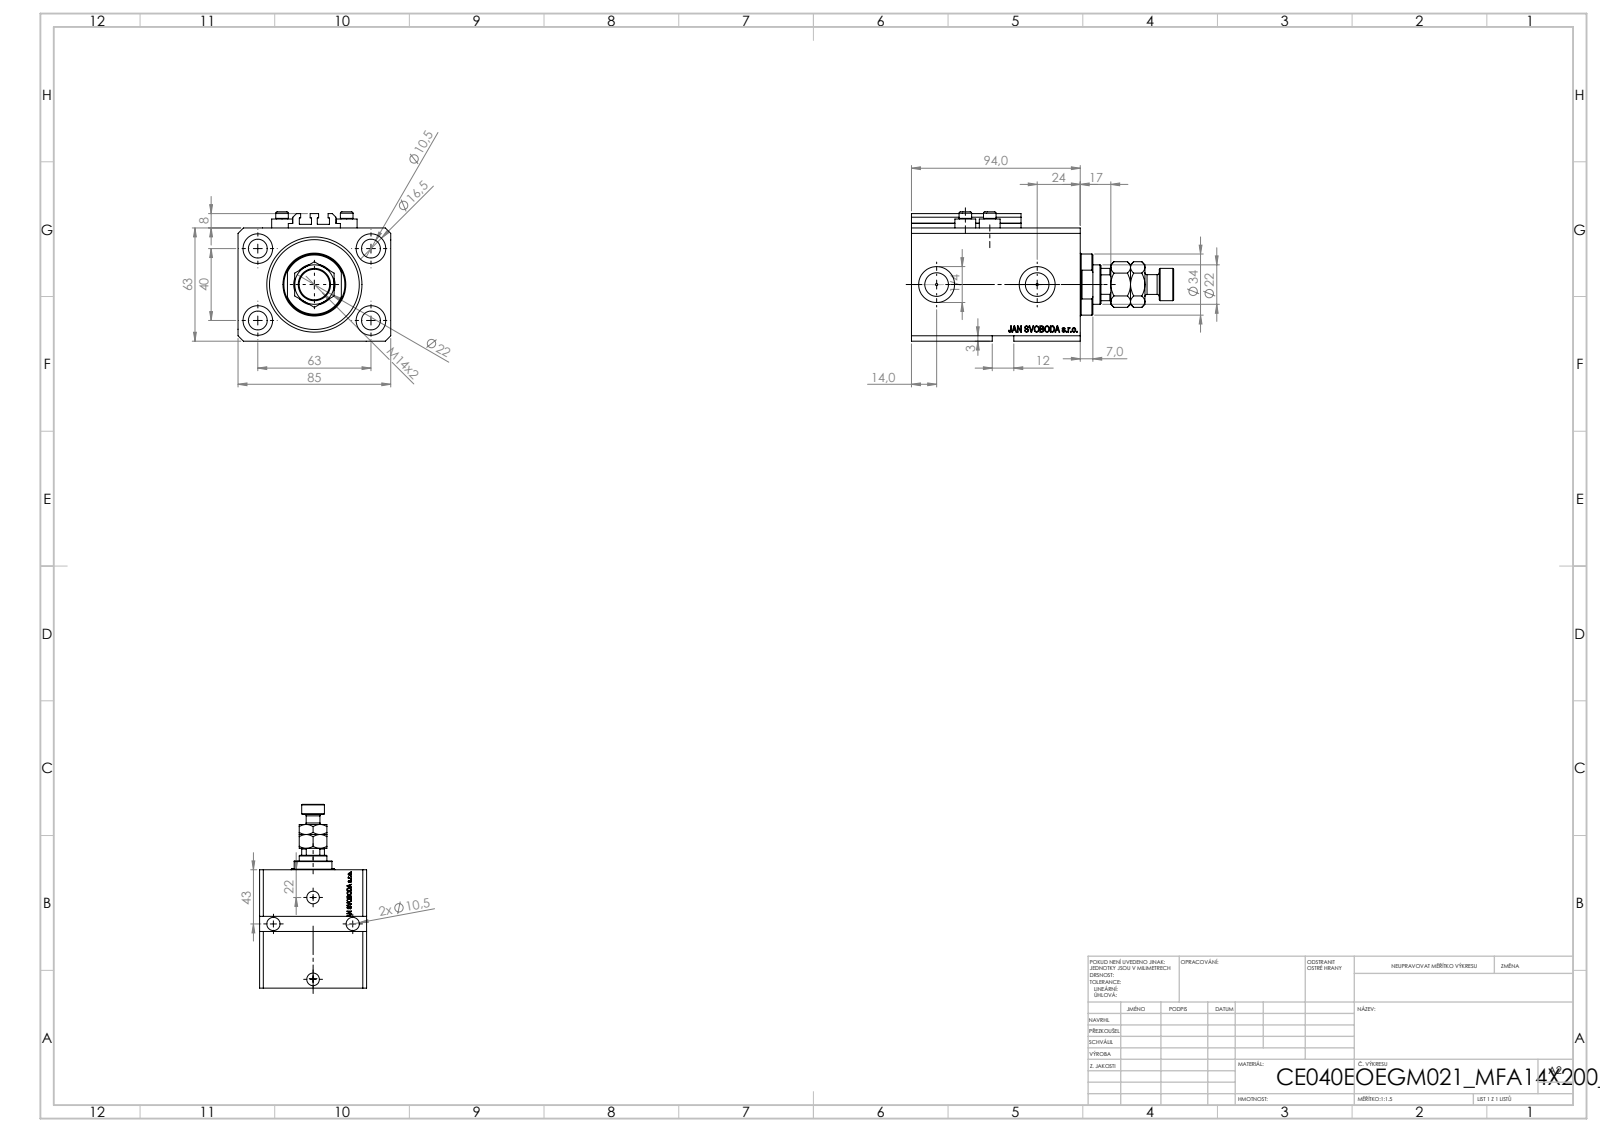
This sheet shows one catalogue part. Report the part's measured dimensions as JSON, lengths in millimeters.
{"part_name": "ALLEN BOLT V250CE; MFA; V250CE_E_Body; V250CE_C_VCP (+1 more)", "step_written_by": "SolidWorks 2019 (CONFIG_CONTROL_DESIGN)", "units": "millimeters", "bodies": {"solids": 9, "faces": 1139, "planar": 551, "cylindrical": 130, "other": 458}, "overall_size": [146, 85, 72], "volume_mm3": 452181, "surface_area_mm2": 99734, "round_holes": [[10.5, 6], [1.25, 4], [4, 4], [16.5, 4], [10, 2], [13.16, 2], [20, 2], [12.5, 1], [22, 1], [40, 1], [53, 1]], "round_bosses_or_shafts": [[11.6, 4], [7, 4], [34, 1], [18, 1], [11, 1]], "partial_cylinders_radius": [[0.2, 10], [10.5, 1]], "face_to_face_distances": [63, 85, 17, 94, 77, 65.6, 11.4, 82.6, 3, 45], "hole_center_spacings": [37.31, 63, 13.6, 15.4, 24.96, 28.79, 29.21, 33.62]}
